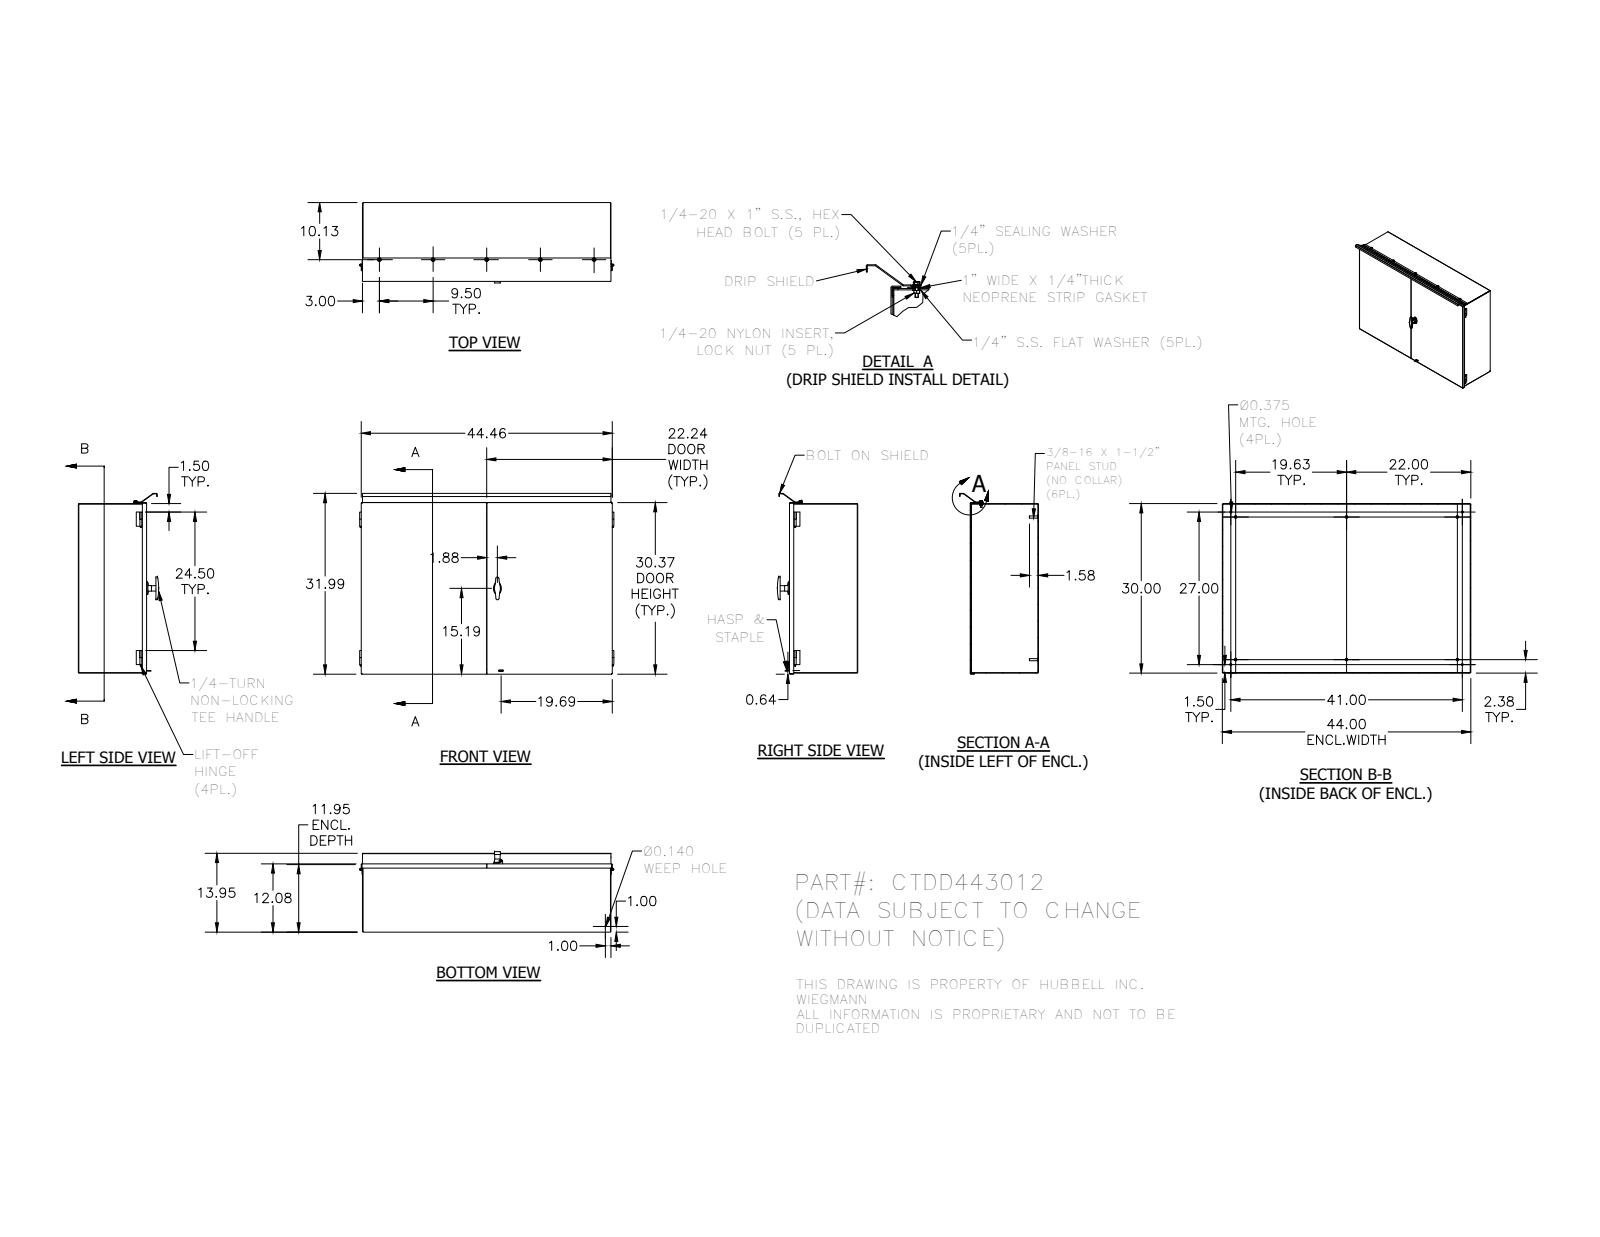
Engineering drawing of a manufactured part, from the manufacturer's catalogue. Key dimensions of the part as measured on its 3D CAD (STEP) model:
Part name (STEP PRODUCT): CTDD443012BTB; CTDD3012LRS; 38822; HC2527 (+8 more)
STEP written by: Autodesk Inventor 2014 (AUTOMOTIVE_DESIGN)
Units: millimetres
Bodies: 63 solids, 1073 faces (611 planar, 220 cylindrical, 242 other)
Overall size (bounding box): 1143 × 812.67 × 361.56
Volume: 7 898 000 mm³ · Surface area: 6 699 000 mm²
Round holes (diameter × count): ⌀4.98 ×7, ⌀7.14 ×7, ⌀5.97 ×5, ⌀6.99 ×5, ⌀7.37 ×5, ⌀9.52 ×5, ⌀4.06 ×2, ⌀5.36 ×2, ⌀5.56 ×2, ⌀6.35 ×2, ⌀7.14 ×2, ⌀2.38 ×1
Round bosses / shafts (diameter × count): ⌀11.13 ×7, ⌀6.35 ×7, ⌀11.73 ×6, ⌀9.52 ×6, ⌀16.51 ×5, ⌀15.88 ×5, ⌀15.24 ×5, ⌀6.6 ×5
Partial cylindrical surfaces — rounded edges, fillets, slot ends (radius × count): R0.79 ×23, R3.17 ×13, R1.59 ×6, R2.67 ×6, R3.17 ×6, R0.2 ×2, R1.59 ×2, R3.97 ×2
Main face-to-face distances: 2.38, 304.4, 302.02, 306.78, 759.62, 762, 757.24, 2.37, 1112.85, 1115.23
Hole centre spacings: 241.3, 482.6, 19.05, 573.06, 584.04, 595.42, 654.38, 664.01
